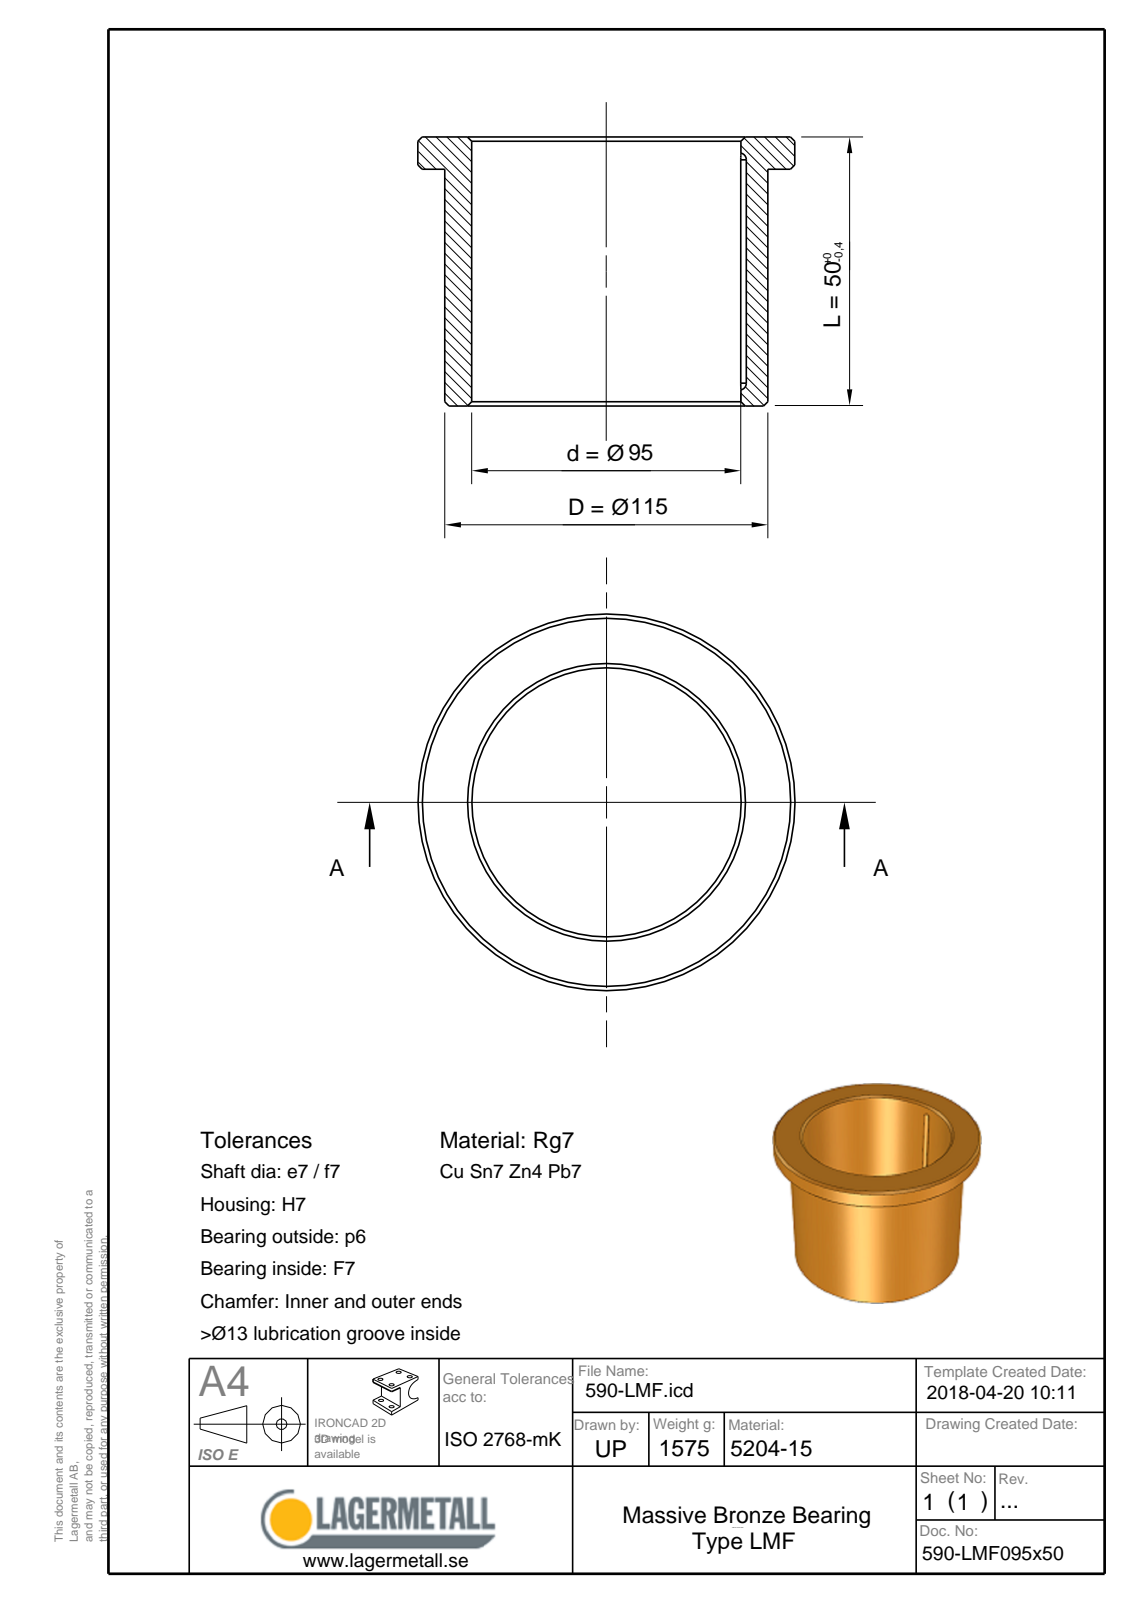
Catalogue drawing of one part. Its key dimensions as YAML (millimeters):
part_name: "590-LMF095x50"
step_written_by: "Spatial InterOp 3D (CONFIG_CONTROL_DESIGN)"
units: millimeters
bodies: {solids: 1, faces: 16, planar: 4, cylindrical: 5, other: 7}
overall_size: [125, 125, 50]
volume: 178979
surface_area: 42651
round_holes:
  - {diameter: 95, count: 1}
round_bosses_or_shafts:
  - {diameter: 125, count: 1}
  - {diameter: 115, count: 1}
partial_cylinders:
  - {radius: 1.75, count: 2}
face_to_face_distances: [50, 42, 8]
